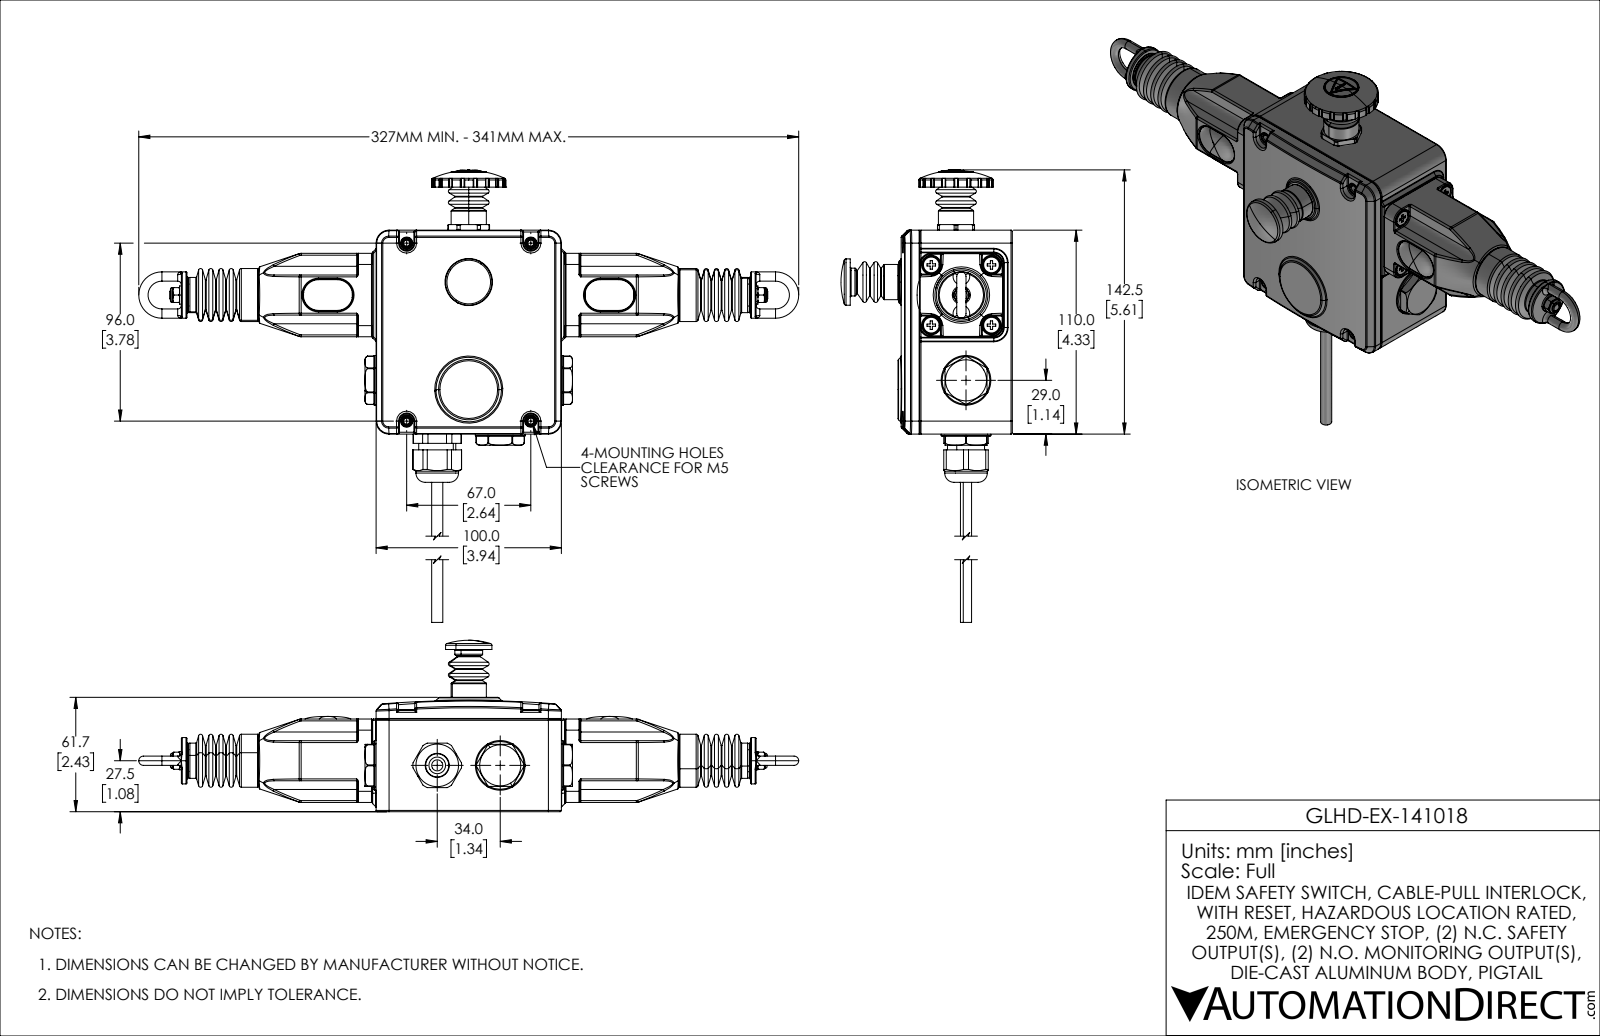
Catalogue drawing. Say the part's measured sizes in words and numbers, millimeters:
The part is named "GLHD-EX-141018". Its 3-D file was written by "SolidWorks 2021 (AUTOMOTIVE_DESIGN)". It is 38 solids with 4515 faces: 1029 planar, 1520 cylindrical and 1966 other. Overall it measures 356.2 by 233.5 by 92.5 millimeters. Its volume is 355 400 cubic millimeters and its surface area 219 500 square millimeters. Round holes: 11 of diameter 5, 6 of diameter 9, 5 of diameter 5.3, 4 of diameter 2.4, 4 of diameter 3.3, 4 of diameter 4, 4 of diameter 4.8, 4 of diameter 5.4, 4 of diameter 5.8, 4 of diameter 9.5, 3 of diameter 3, 3 of diameter 4.4. Round bosses or shafts: 8 of diameter 6, 4 of diameter 8.5, 4 of diameter 4.4, 3 of diameter 19, 3 of diameter 5, 2 of diameter 26.8, 2 of diameter 25, 2 of diameter 19.4. Partial cylindrical surfaces (rounded edges, fillets, slot ends): 266 of radius 0.5, 114 of radius 1, 88 of radius 0.2, 72 of radius 0.7, 26 of radius 0.3, 15 of radius 0.1, 14 of radius 0.2, 14 of radius 2. The main face-to-face distances are 54.8, 3.5, 2.9, 51.9, 45, 110, 11.7, 4, 98.5, 2. The hole center spacings are 9.5, 23, 32.5, 48, 48.6, 76.5, 88.6, 96.
